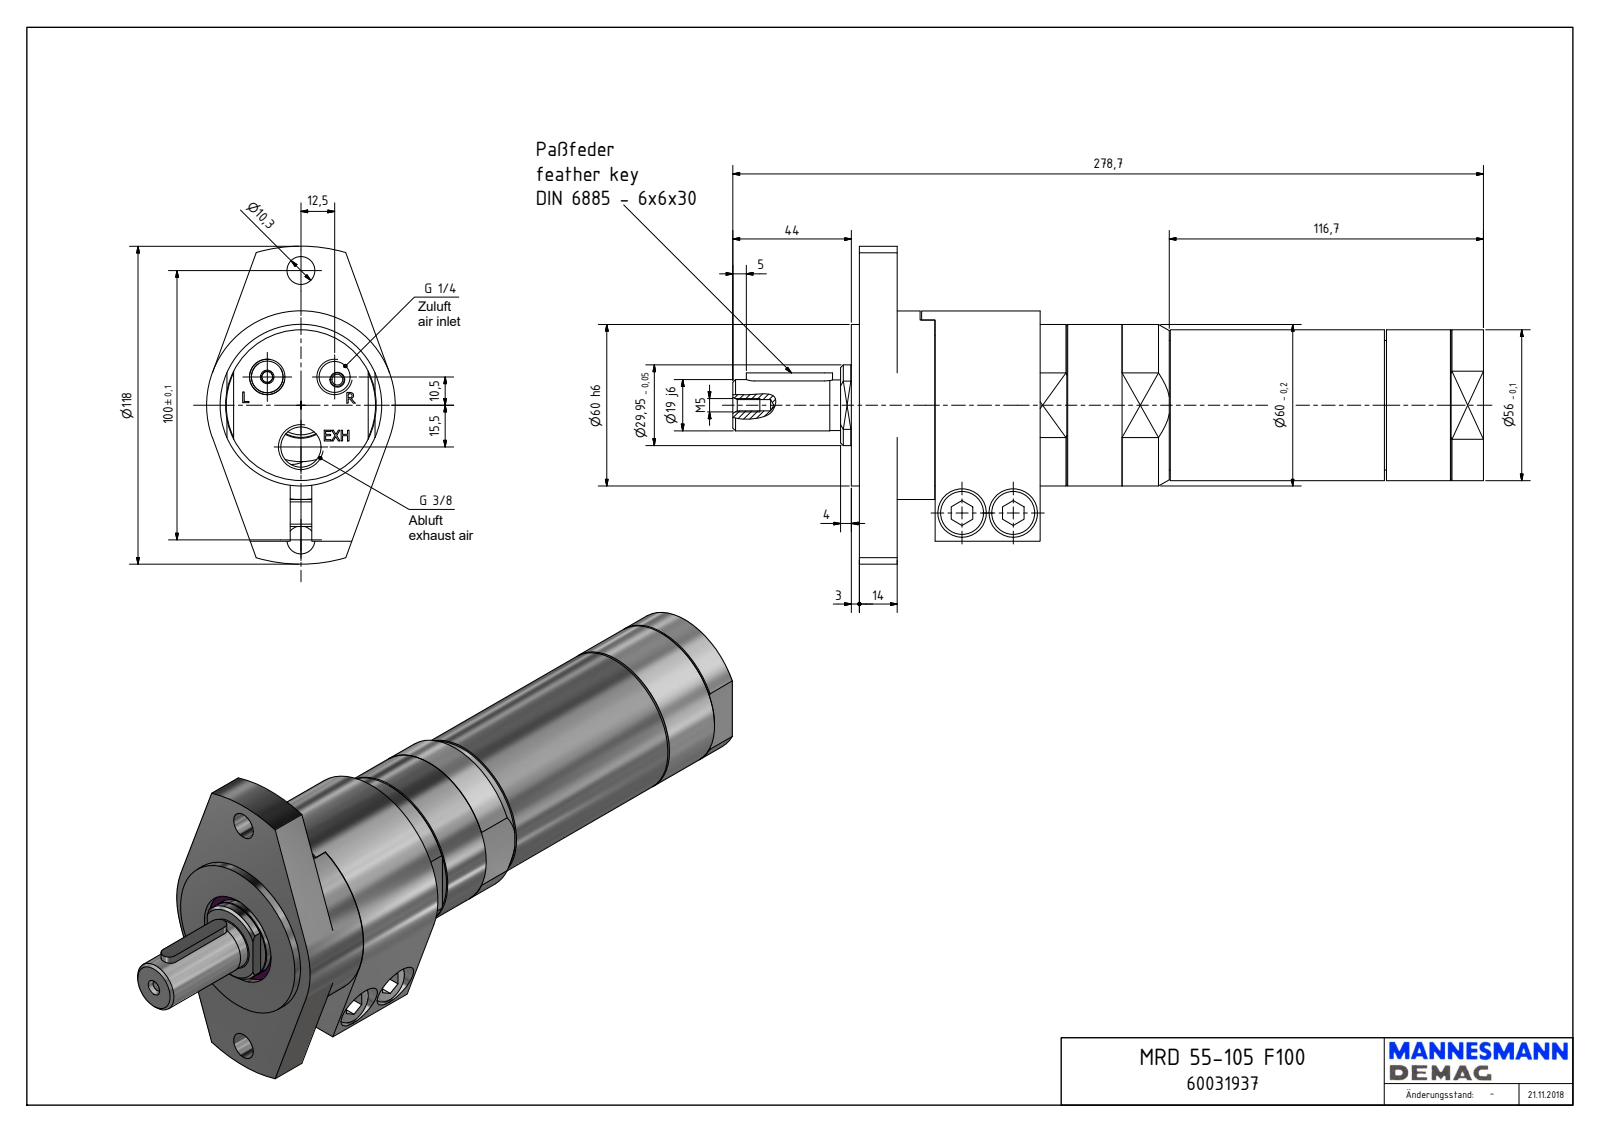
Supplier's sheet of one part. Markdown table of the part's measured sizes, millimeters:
| quantity | value |
| --- | --- |
| part name | MRD 55-105 F100_60031937 |
| STEP written by | Autodesk Inventor 2018 (AUTOMOTIVE_DESIGN) |
| units | millimeters |
| bodies | 1 solid, 285 faces (166 planar, 64 cylindrical, 55 other) |
| overall size | 278.7 × 118 × 70 |
| volume | 748 783 mm³ |
| surface area | 82 203 mm² |
| round holes (diameter × count) | 4 × 2, 8.38 × 2, 10.3 × 2, 10.5 × 2, 18 × 2, 1.55 × 1, 4.13 × 1, 5.5 × 1, 11.45 × 1, 14.95 × 1, 35 × 1, 36.5 × 1 |
| round bosses / shafts (diameter × count) | 16 × 2, 10 × 2, 70 × 1, 60 × 1, 56 × 1, 55.18 × 1, 48.18 × 1, 29.95 × 1 |
| partial cylindrical surfaces (radius × count) | 3 × 2, 6 × 2, 5.72 × 1, 19.67 × 1, 23 × 1, 26.48 × 1, 59 × 1 |
| main face-to-face distances | 14, 17, 3, 231.7, 217.7, 234.7, 70.1, 67.1, 53.1, 164.6 |
| hole center spacings | 16.32, 28.85, 41.43, 50, 61.78, 15.5, 19, 25 |
